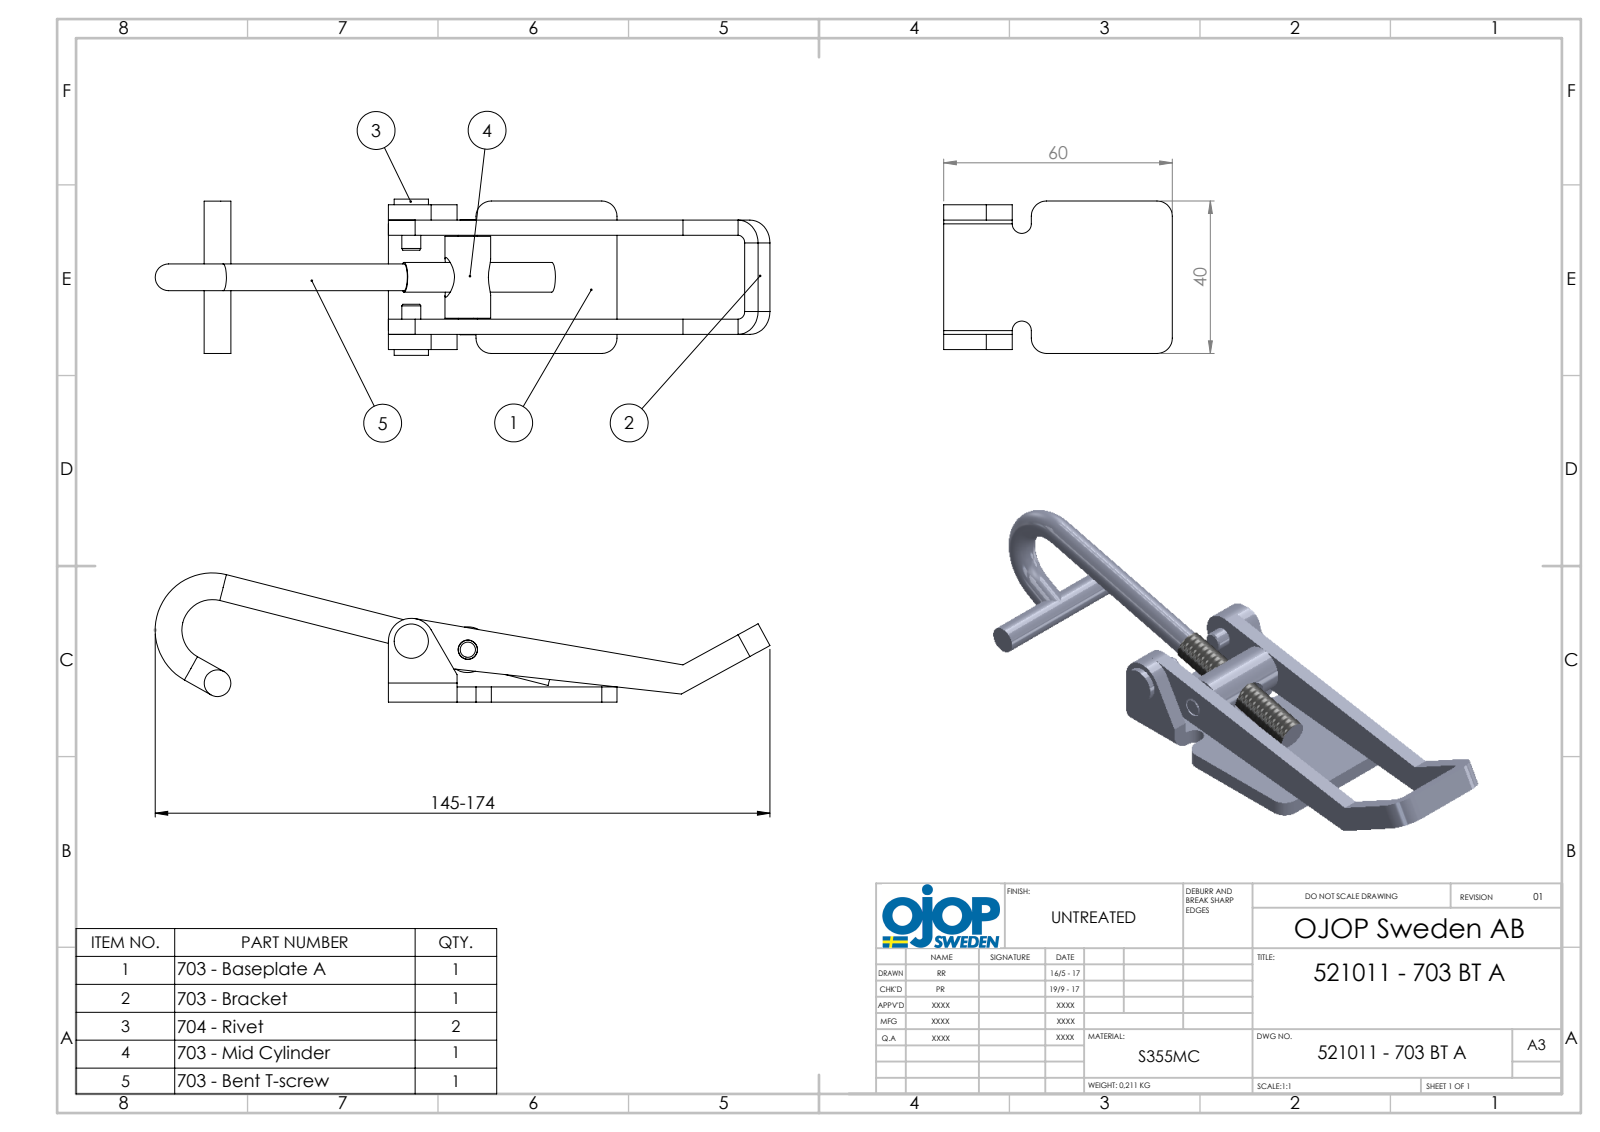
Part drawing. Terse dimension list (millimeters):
name: 521011 - 703 BT A; 74086 - Böjd T-skruv 703 RF; 703 - Mid Cylinder; 704 - Rivet Gradin (+2 more)
written by: SolidWorks 2015 (AUTOMOTIVE_DESIGN)
unit: mm
bodies: 6 solids, 131 faces (58 planar, 59 cylindrical, 14 other)
size: 161.38 × 41 × 33.9
volume: 27 773 mm³; area: 18 332 mm²
holes: 2× ⌀5.1, 1× ⌀7.2, 1× ⌀7.7
bosses: 4× ⌀7, 2× ⌀5, 1× ⌀12, 1× ⌀9, 1× ⌀7.8
rounds: 4× R4, 3× R6, 2× R1, 2× R2, 2× R2.5, 2× R5
face distances: 4, 26, 30, 22, 8, 34, 5, 1, 9, 31
hole spacings: 15.01
